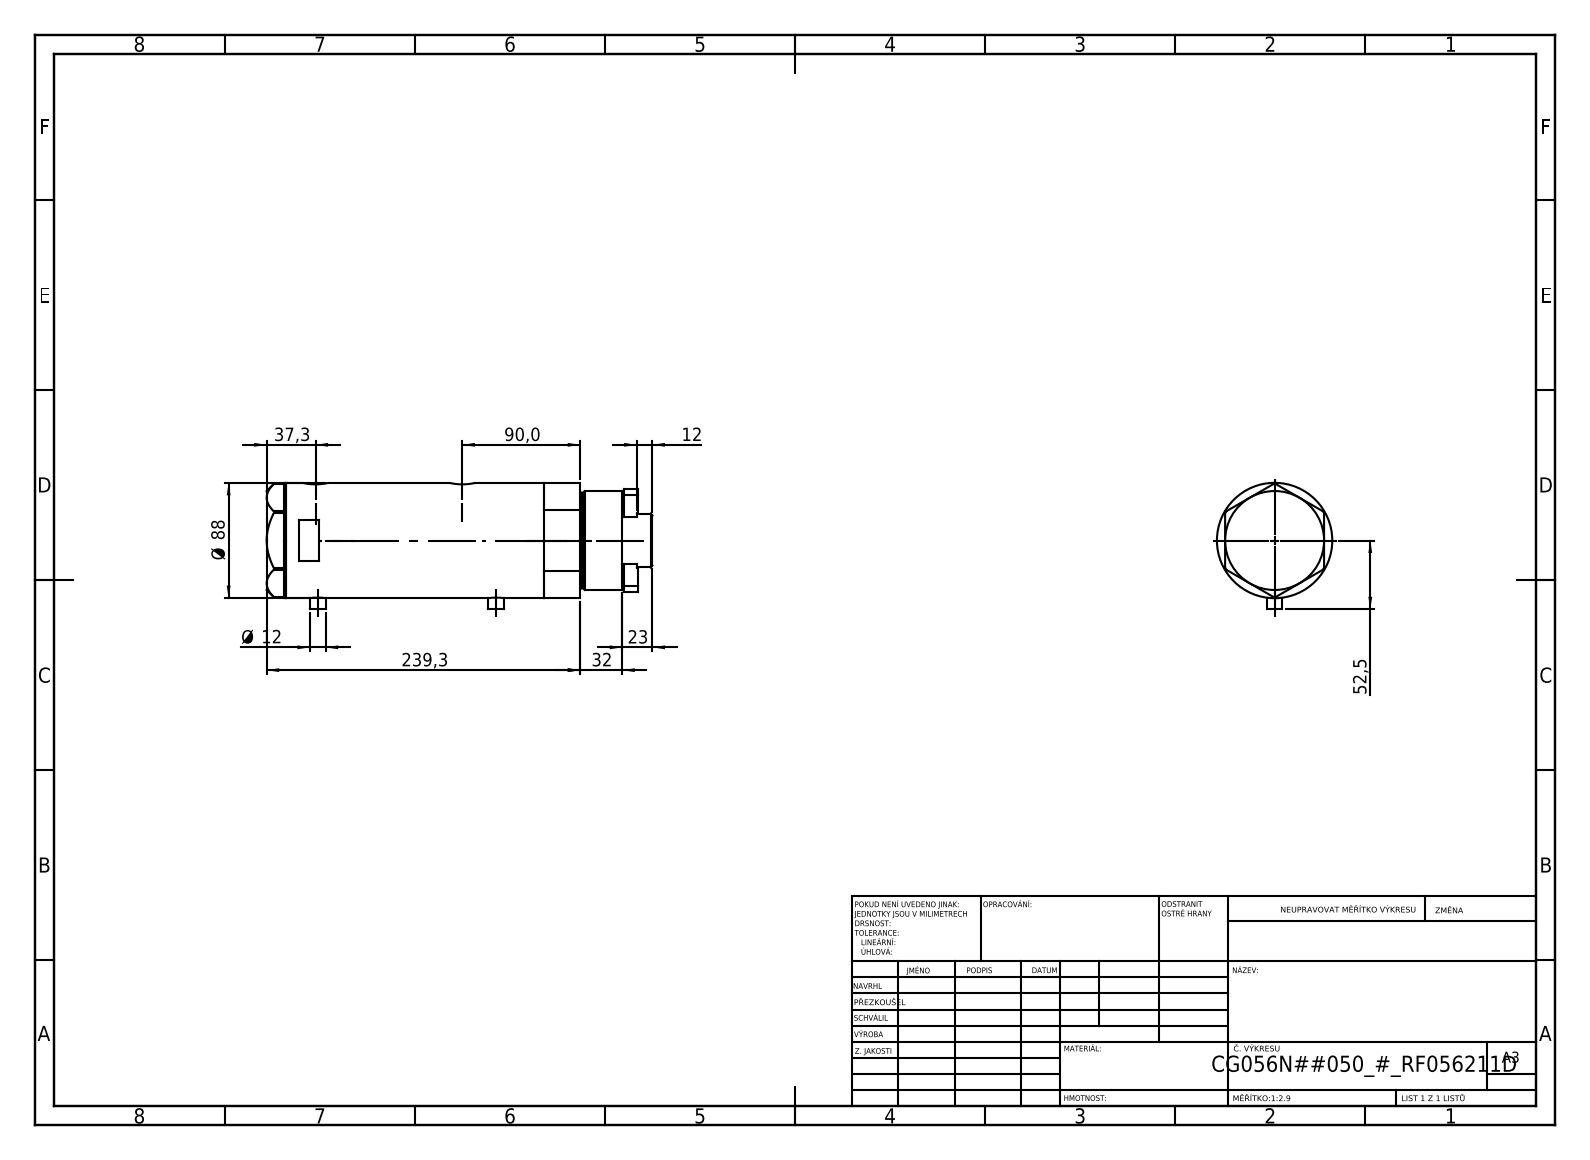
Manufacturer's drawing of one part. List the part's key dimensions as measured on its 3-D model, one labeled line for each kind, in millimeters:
Part name (STEP PRODUCT): V270CG_BACK; V270CG_MIDDLE; V270CG_FRONT; V270CG_VC (+1 more)
STEP written by: SolidWorks 2019 (CONFIG_CONTROL_DESIGN)
Units: millimetres
Bodies: 6 solids, 161 faces (76 planar, 65 cylindrical, 20 other)
Overall size (bounding box): 294.3 × 96.5 × 88
Volume: 1 545 000 mm³ · Surface area: 228 069 mm²
Round holes (diameter × count): ⌀8.1 ×4, ⌀13.5 ×4, ⌀12.5 ×2, ⌀13.16 ×2, ⌀20 ×2, ⌀14.5 ×1, ⌀42 ×1, ⌀43.5 ×1, ⌀56 ×1, ⌀60 ×1, ⌀80 ×1
Round bosses / shafts (diameter × count): ⌀12 ×2, ⌀88 ×1, ⌀75 ×1, ⌀73 ×1, ⌀41 ×1
Main face-to-face distances: 134.4, 26, 108.4, 15, 41, 149.4, 256.3, 271.3, 230.3, 121.9
Hole centre spacings: 30.35, 18, 57.96, 60.69, 1.7, 25.8, 110.3, 112
